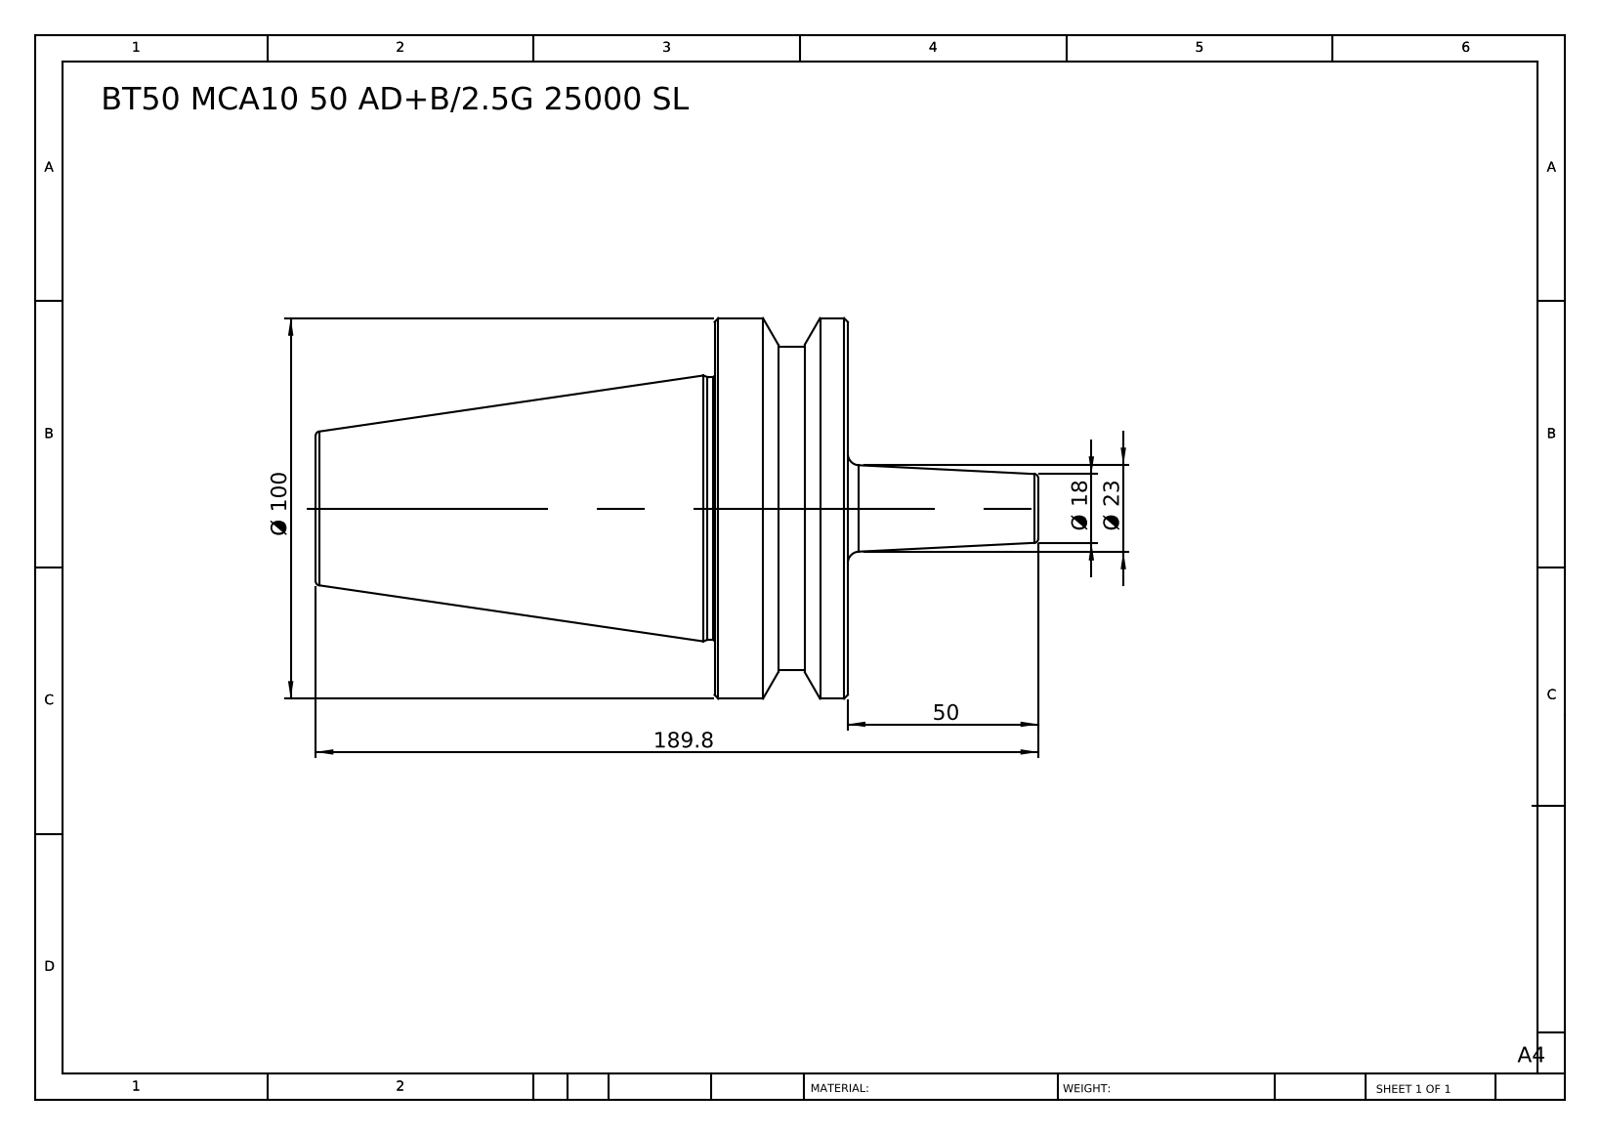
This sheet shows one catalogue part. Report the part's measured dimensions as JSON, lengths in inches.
{"part_name": "BT50 MCA10 50 AD+B-2.5G 25000 SL", "step_written_by": "SolidWorks 2014 (CONFIG_CONTROL_DESIGN)", "units": "inches", "bodies": {"solids": 1, "faces": 36, "planar": 6, "cylindrical": 8, "other": 22}, "overall_size": [7.472, 3.937, 3.937], "volume_in3": 32.14, "surface_area_in2": 73.35, "round_bosses_or_shafts": [[3.937, 1], [3.346, 1], [2.717, 1]], "face_to_face_distances": [1.378, 5.504, 4.126, 1.969, 3.346, 7.472, 2.413, 0.445, 0.933, 5.059]}
